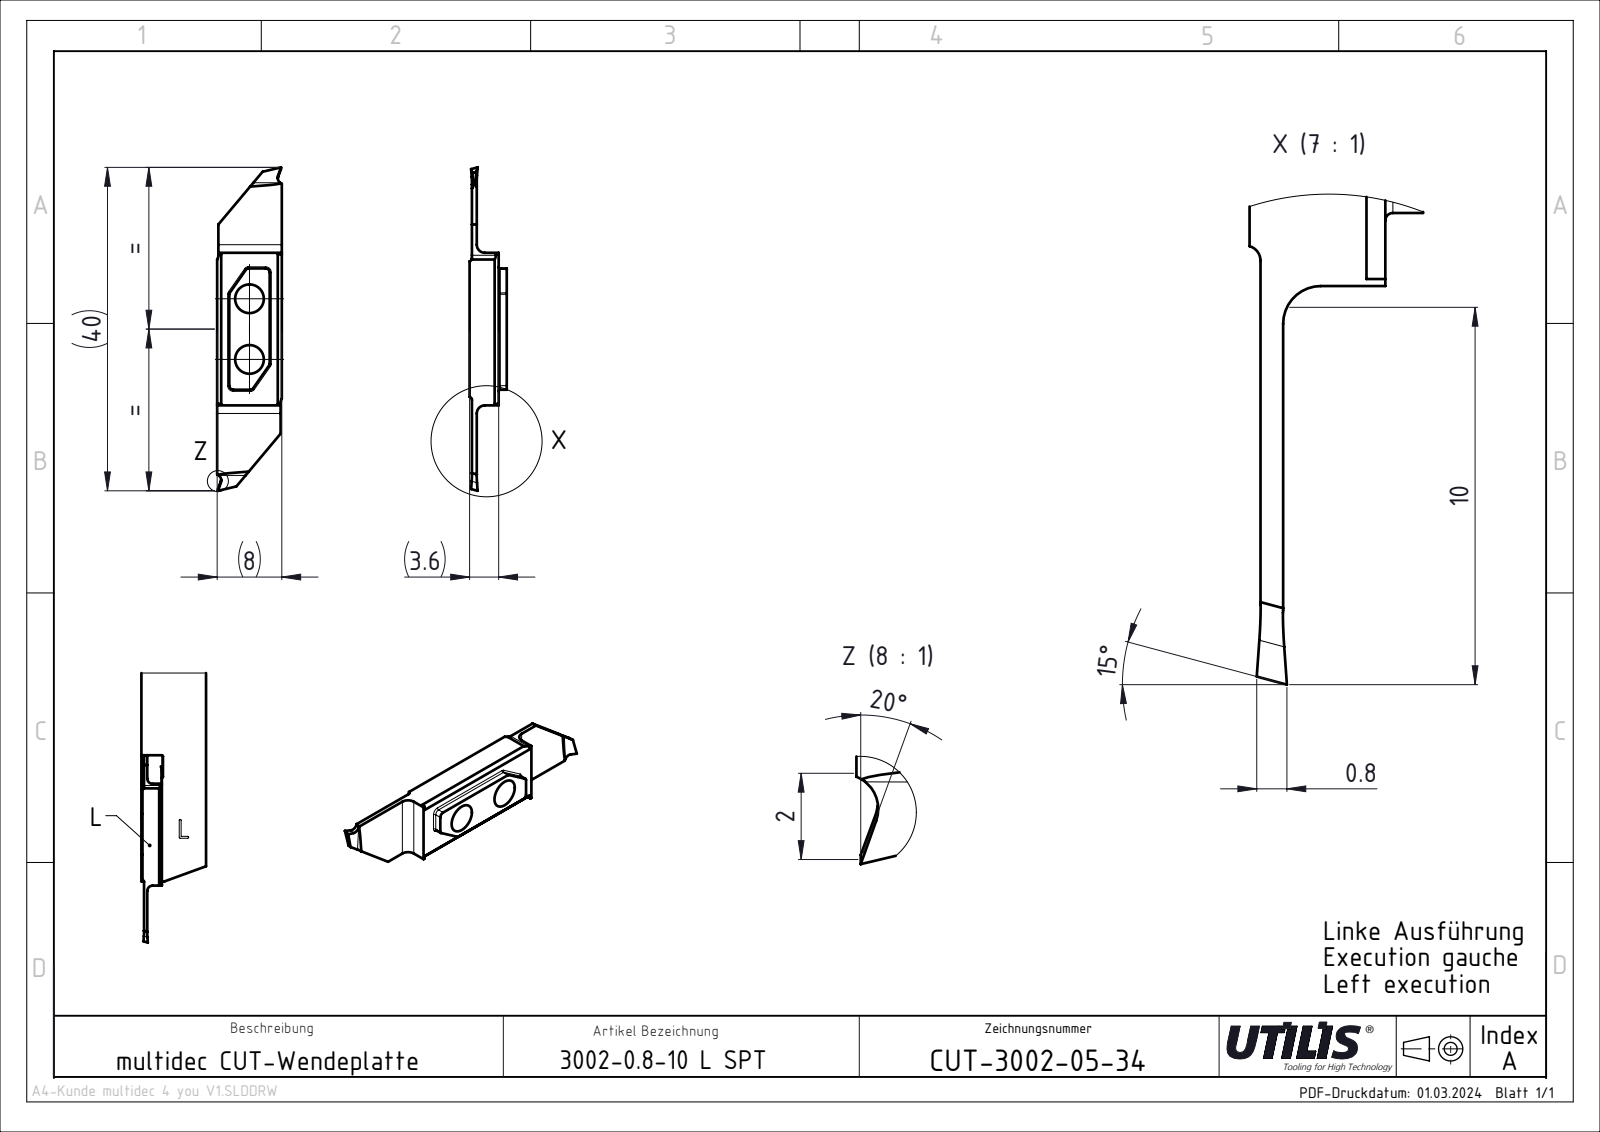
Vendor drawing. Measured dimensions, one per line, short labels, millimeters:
name: CUT-3002 SPT Slim_and_Deep; ASME Y14.5
written by: SolidWorks 2023 SP4 || FormatWorks Professional (AP242_MANAGED_MODEL_BASED_3D_ENGINEERING_MIM_LF)
unit: mm
bodies: 1 solid, 36 faces (26 planar, 10 cylindrical, 0 other)
size: 40 × 8 × 3.6
volume: 541 mm³; area: 785 mm²
holes: 2× ⌀3.55
rounds: 4× R1, 2× R0.4
face distances: 3.6, 3.31, 0.89, 0.6, 2.71, 8, 18.88, 1.27, 7.85, 22.54
hole spacings: 7.5
